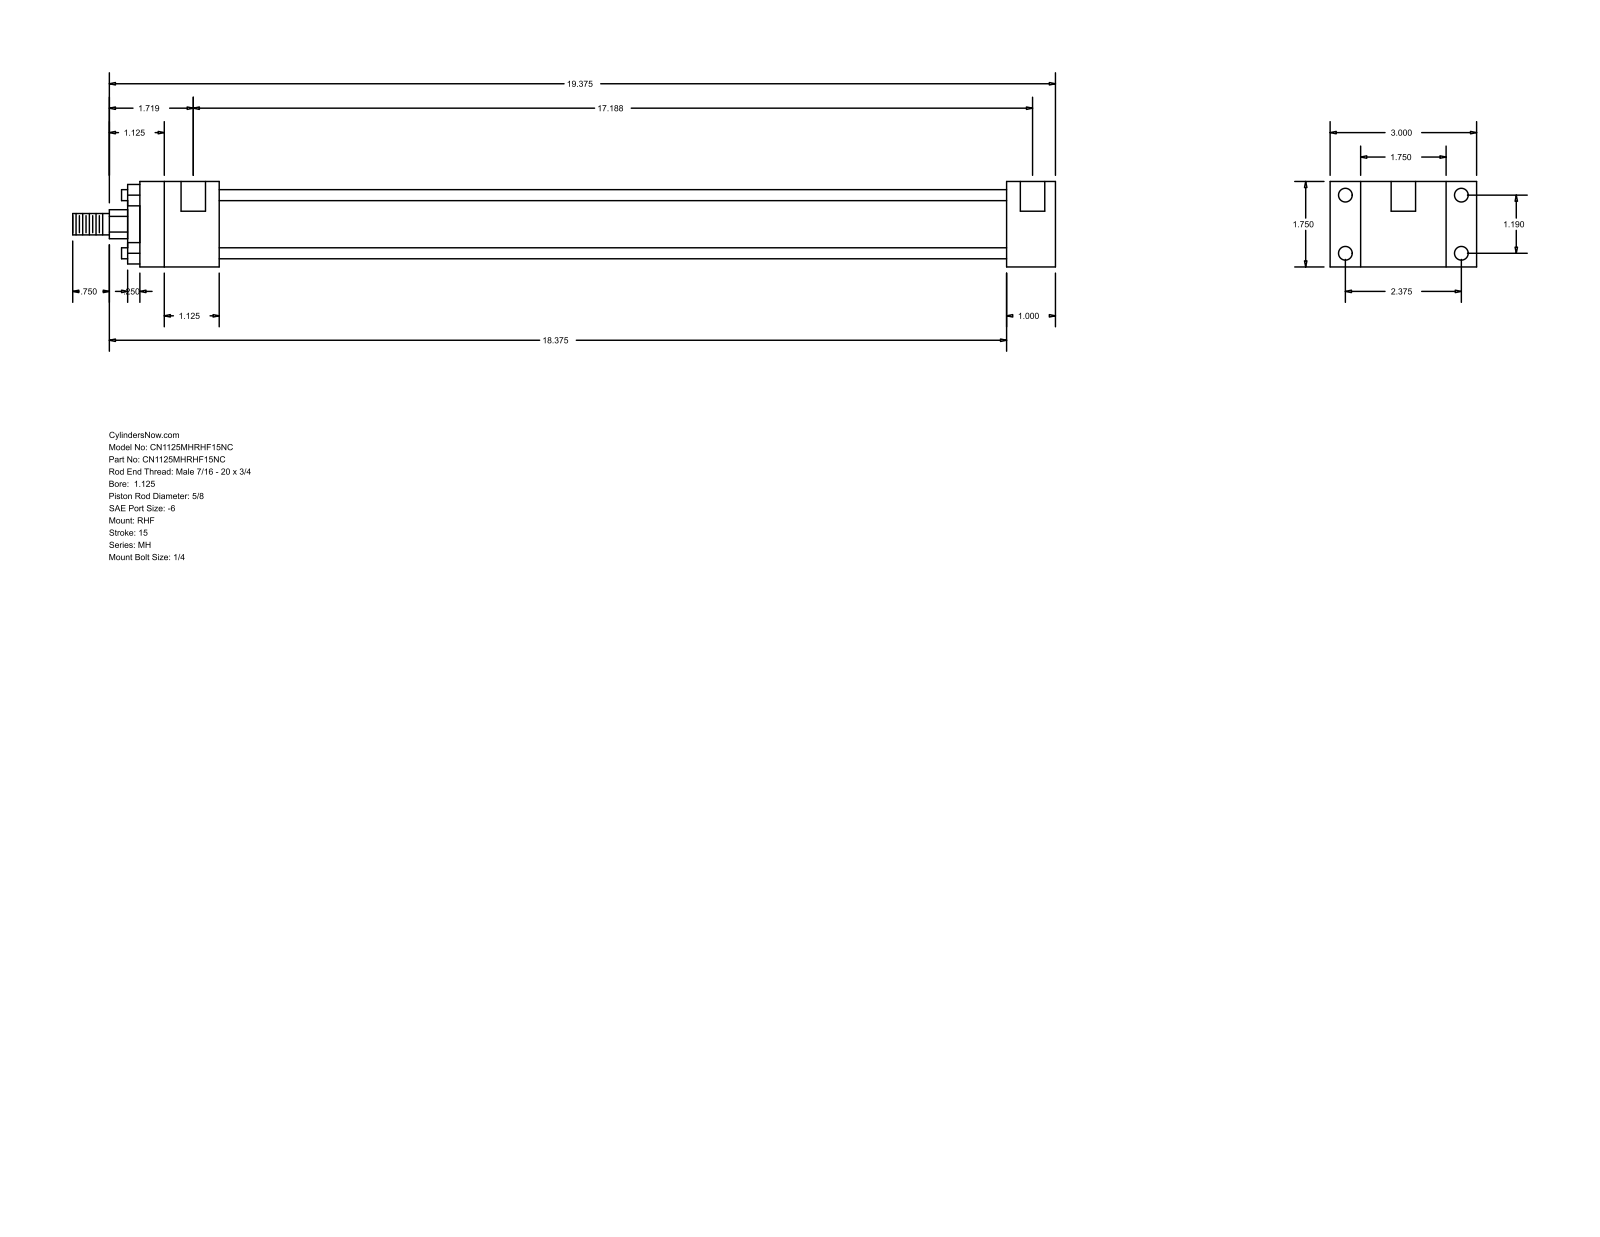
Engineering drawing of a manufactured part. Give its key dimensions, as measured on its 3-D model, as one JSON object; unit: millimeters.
{"part_name": "MH_RHF__0112_0.625", "step_written_by": "GSSL Pune (CONFIG_CONTROL_DESIGN)", "units": "millimeters", "bodies": {"solids": 0, "faces": 88, "planar": 60, "cylindrical": 28, "other": 0}, "overall_size": [511.18, 76.2, 44.45], "round_holes": [[5.56, 4], [7.14, 4], [12.7, 2]], "round_bosses_or_shafts": [[5.71, 4], [34.92, 1], [28.57, 1], [15.88, 1], [11.11, 1]], "partial_cylinders_radius": [[7.54, 1]], "face_to_face_distances": [44.46, 15.87, 60.33, 25.39, 76.2, 409.58, 434.97, 41.27, 450.85, 476.24], "hole_center_spacings": [30.22, 60.32, 67.47, 433.39, 3.17, 436.56]}
